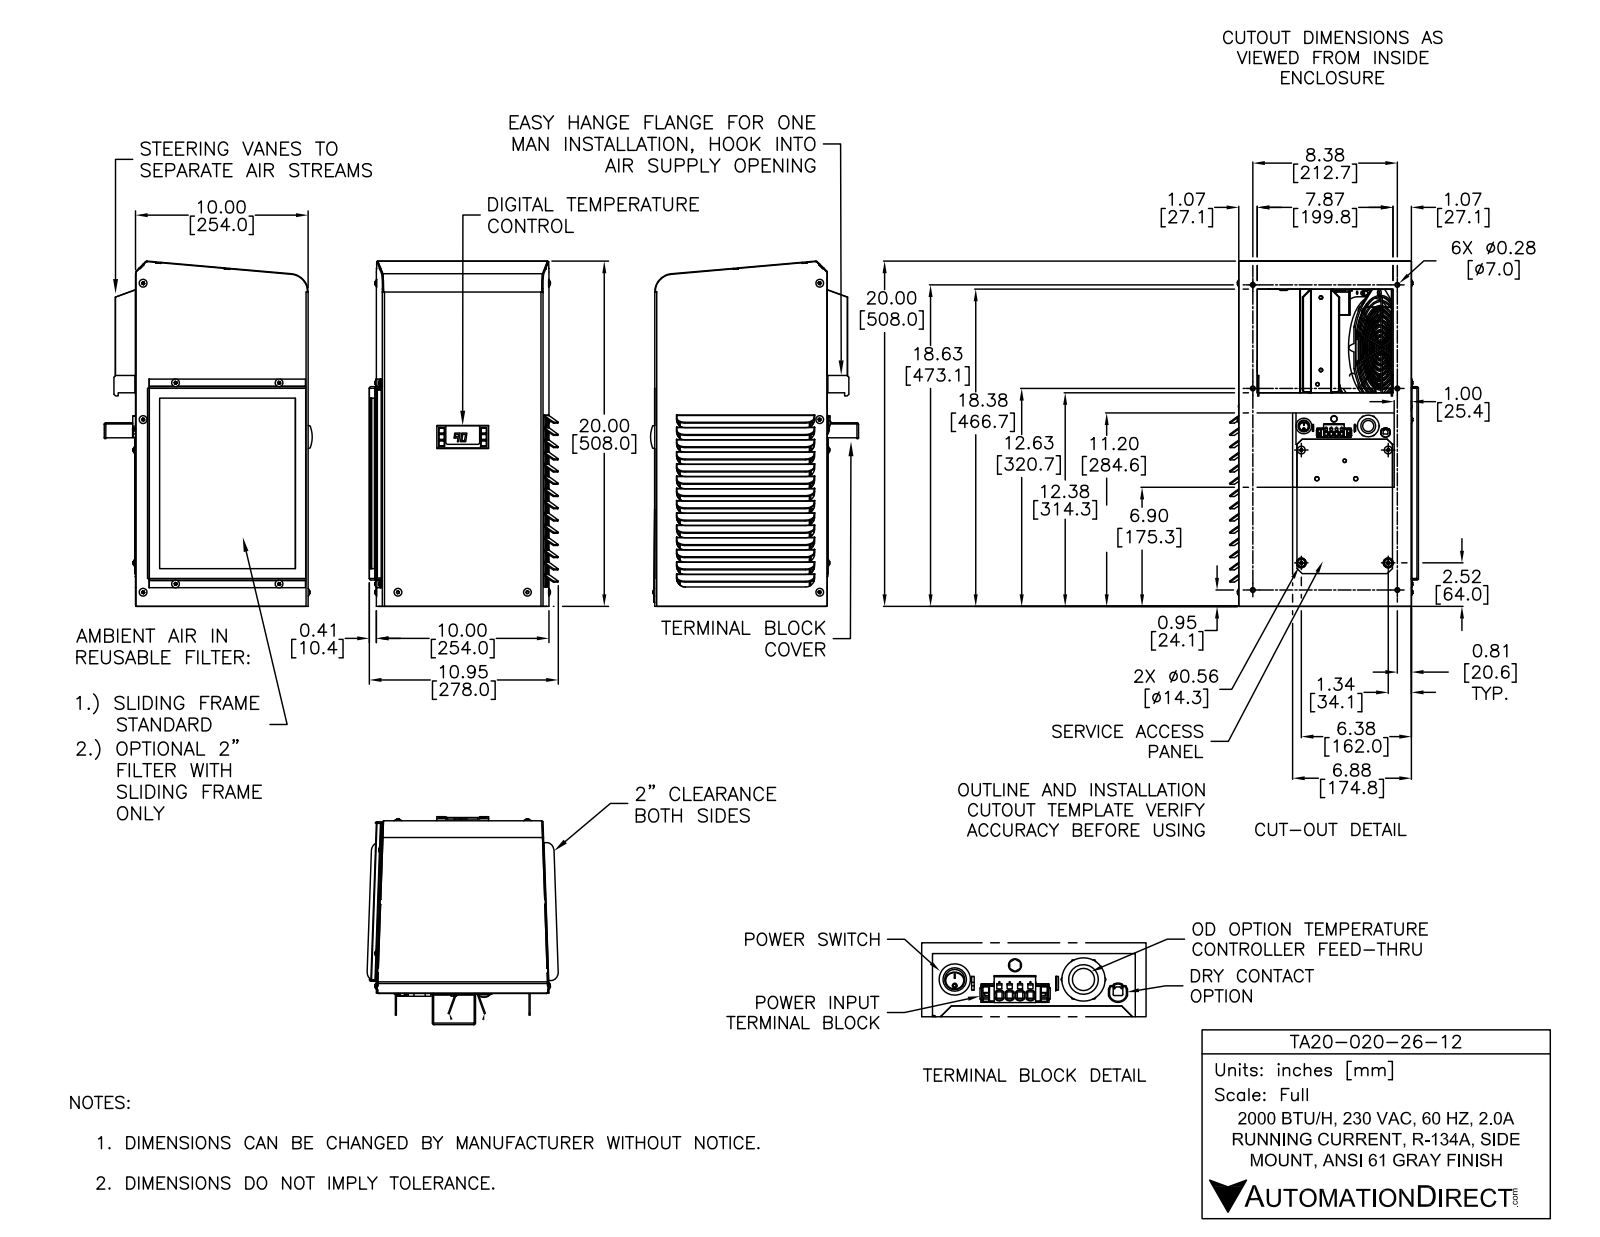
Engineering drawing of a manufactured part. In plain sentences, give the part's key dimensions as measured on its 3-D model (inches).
The part is named "TA20-020-26-12". Its 3-D file was written by "SolidWorks 2019 (AUTOMOTIVE_DESIGN)". It is 52 solids with 2157 faces: 1121 planar, 737 cylindrical and 299 other. Overall it measures 20 by 11.344 by 11.002 inches. Its volume is 401.3 cubic inches and its surface area 2 755 square inches. Round holes: 17 of diameter 0.204, 6 of diameter 0.2, 6 of diameter 0.344, 4 of diameter 0.045, 4 of diameter 0.12, 4 of diameter 0.14, 4 of diameter 0.166, 4 of diameter 0.219, 2 of diameter 0.091, 2 of diameter 0.126, 2 of diameter 0.166, 2 of diameter 0.25. Round bosses or shafts: 16 of diameter 0.19, 6 of diameter 0.44, 2 of diameter 0.36, 2 of diameter 0.106, 1 of diameter 1, 1 of diameter 0.906, 1 of diameter 0.865, 1 of diameter 0.832. Partial cylindrical surfaces (rounded edges, fillets, slot ends): 100 of radius 0.015, 96 of radius 0.01, 44 of radius 0.031, 33 of radius 0.03, 22 of radius 0.1, 16 of radius 0.011, 14 of radius 0.091, 13 of radius 0.089. The main face-to-face distances are 0.06, 0.058, 10, 9.94, 9.942, 9.882, 0.185, 0.244, 2.624, 2.809. The hole center spacings are 0.2, 0.4, 6, 6, 11.65, 13.104, 8.251, 8.375.
